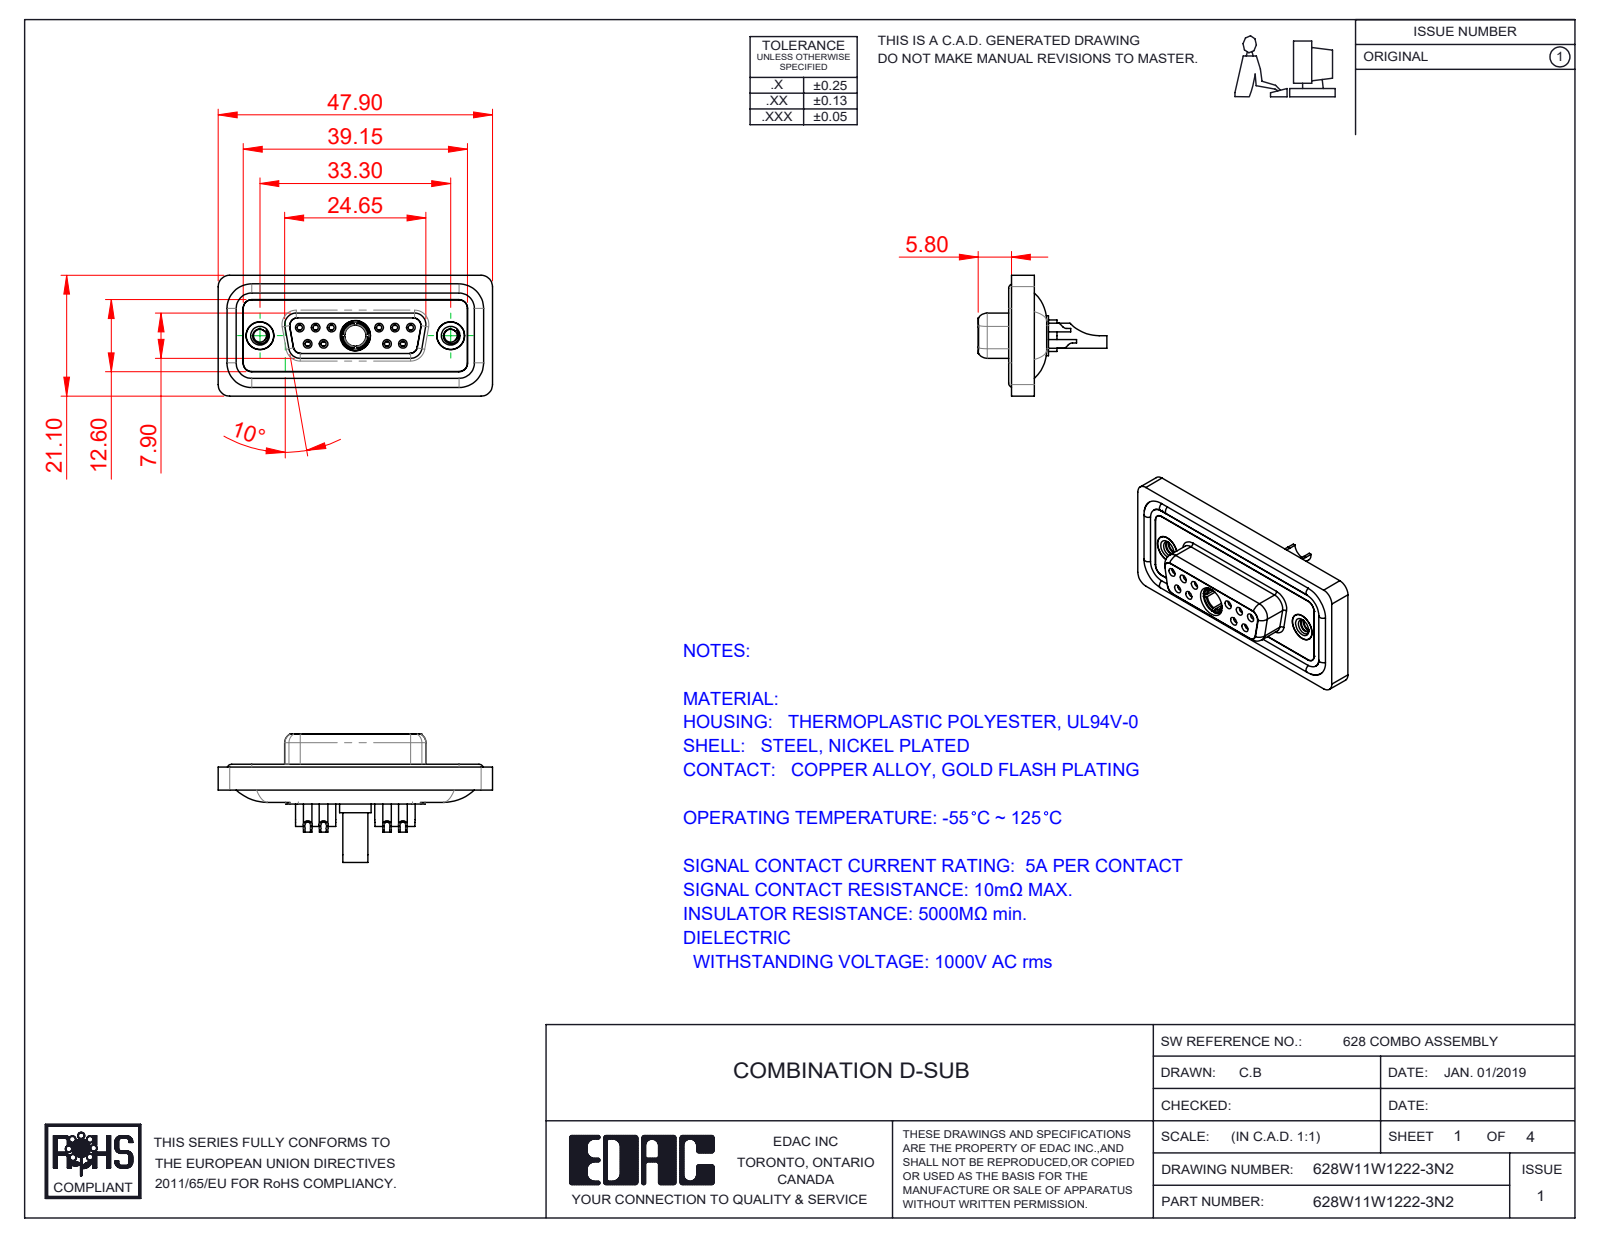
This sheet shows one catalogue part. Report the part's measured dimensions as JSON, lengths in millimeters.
{"part_name": "628Combo Shell Rear_15 Contacts; 628Combo Contact Row 1_22; 628Combo Threaded Rivet_2; 628Combo Contact Row 2_22 (+5 more)", "step_written_by": "SolidWorks 2020 (CONFIG_CONTROL_DESIGN)", "units": "millimeters", "bodies": {"solids": 19, "faces": 1016, "planar": 307, "cylindrical": 424, "other": 285}, "overall_size": [47.9, 22.45, 21.1], "volume_mm3": 6169, "surface_area_mm2": 10240, "round_holes": [[0.9, 10], [1, 10], [1.1, 10], [1.5, 10], [2, 10], [1.7, 6], [1.6, 4], [4.85, 3], [2.26, 2], [4, 2], [4.05, 2], [5, 2]], "round_bosses_or_shafts": [[2.2, 10], [1.6, 10], [4.95, 2], [4.8, 2], [5.5, 1], [5.2, 1], [4.96, 1], [4.75, 1]], "partial_cylinders_radius": [[1.5, 22], [2, 20], [1.35, 12], [1.6, 8], [1, 6], [0.25, 4], [0.5, 4], [0.6, 4]], "face_to_face_distances": [0.4, 1.6, 1.8, 2.9, 0.5, 1.1, 5.65, 7.45, 6.6, 7.05], "hole_center_spacings": [3.16, 2.77, 13.85, 11.08, 16.62, 5.03, 5.04, 5.54]}
